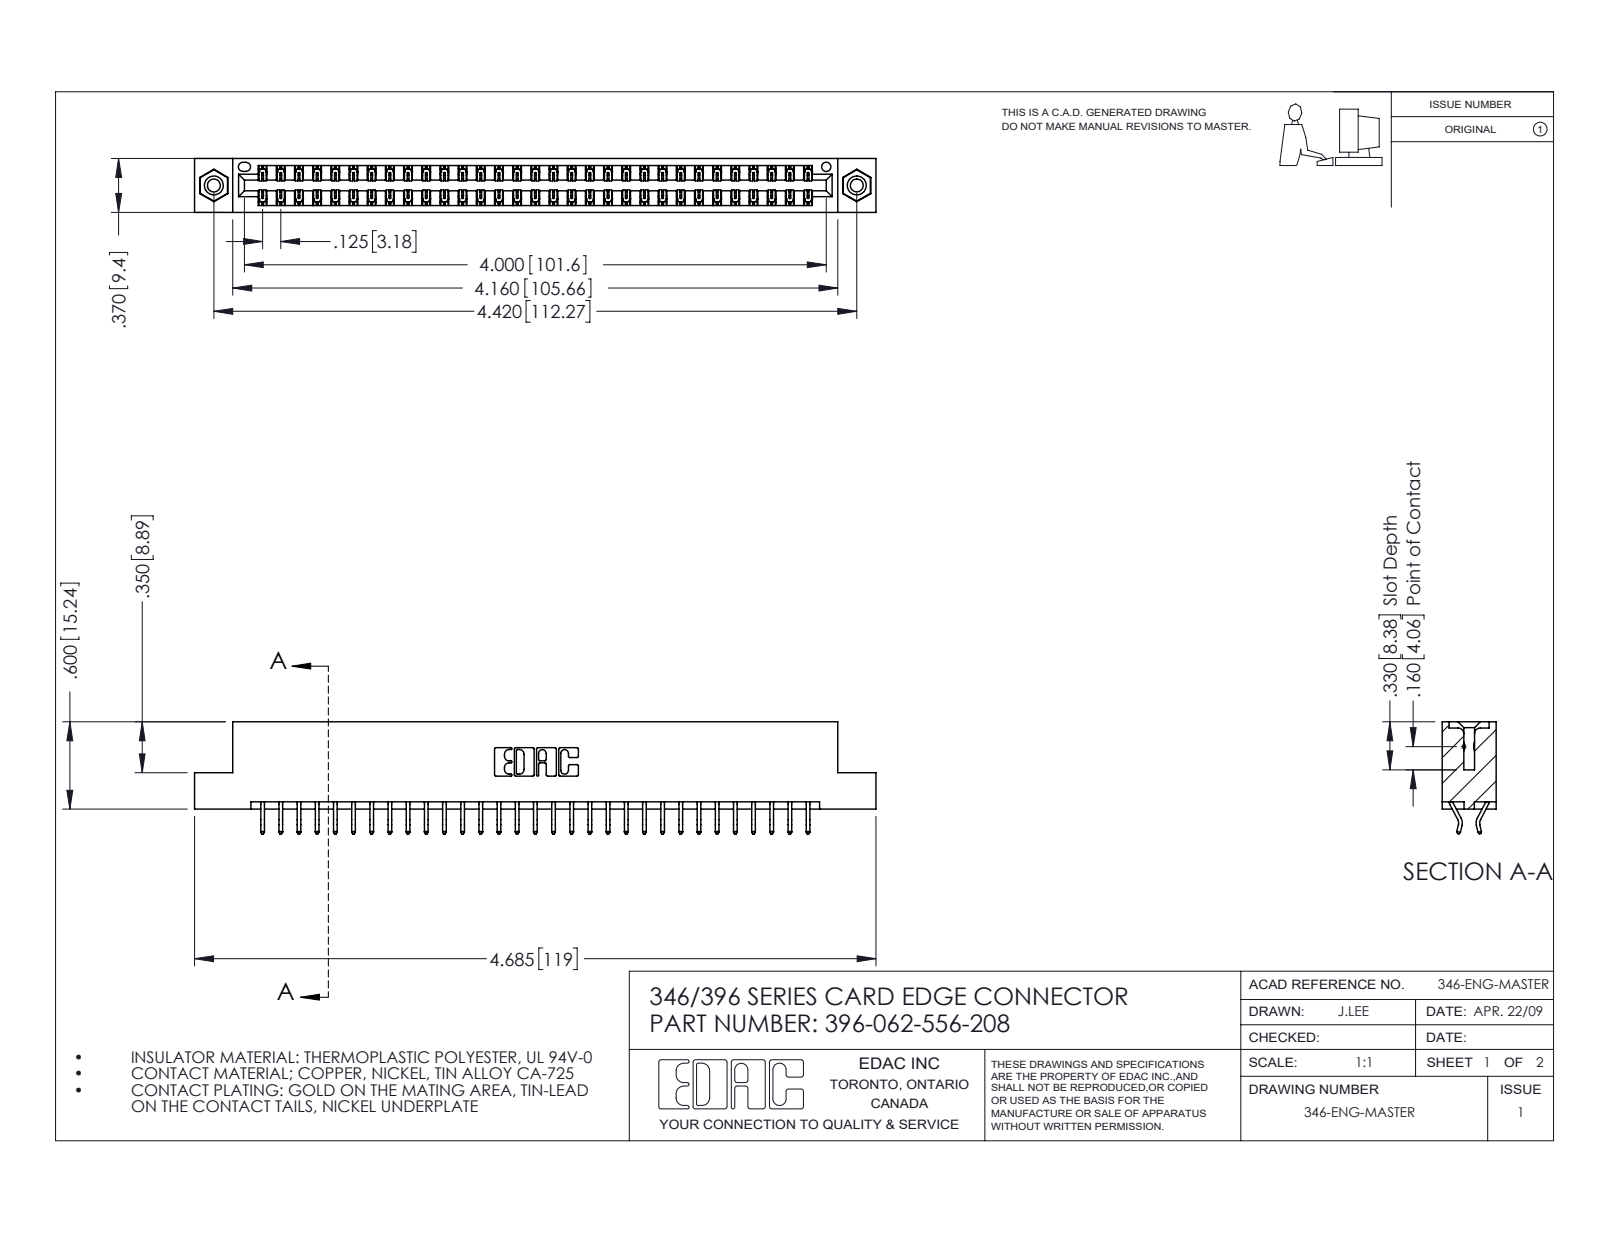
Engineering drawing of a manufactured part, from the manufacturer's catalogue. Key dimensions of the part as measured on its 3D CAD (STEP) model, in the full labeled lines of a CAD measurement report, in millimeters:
Part name (STEP PRODUCT): 346 Part_Flush Mounting Lugs - 0.156 Dia-TI; 396-062-556-208; 345-250-001_345-250-003-102; 345-292-001_556 Tail
STEP written by: SolidWorks 2016 (CONFIG_CONTROL_DESIGN)
Units: millimetres
Bodies: 65 solids, 3778 faces (2526 planar, 1236 cylindrical, 16 other)
Overall size (bounding box): 119 × 19.6 × 9.4
Volume: 11 500 mm³ · Surface area: 15 610 mm²
Round holes (diameter × count): ⌀2.3 ×2, ⌀3.2 ×2, ⌀4 ×2, ⌀1.6 ×1
Round bosses / shafts (diameter × count): ⌀3.9 ×2
Partial cylindrical surfaces — rounded edges, fillets, slot ends (radius × count): R0.2 ×93, R0.3 ×22, R0.2 ×6, R0.8 ×6, R0.7 ×3, R0.3 ×2, R0.4 ×2, R0.6 ×2
Main face-to-face distances: 1.2, 8.2, 9.4, 6.4, 0.6, 1.8, 7.6, 7, 3.8, 5.6
Hole centre spacings: 6.2, 107, 112.3
